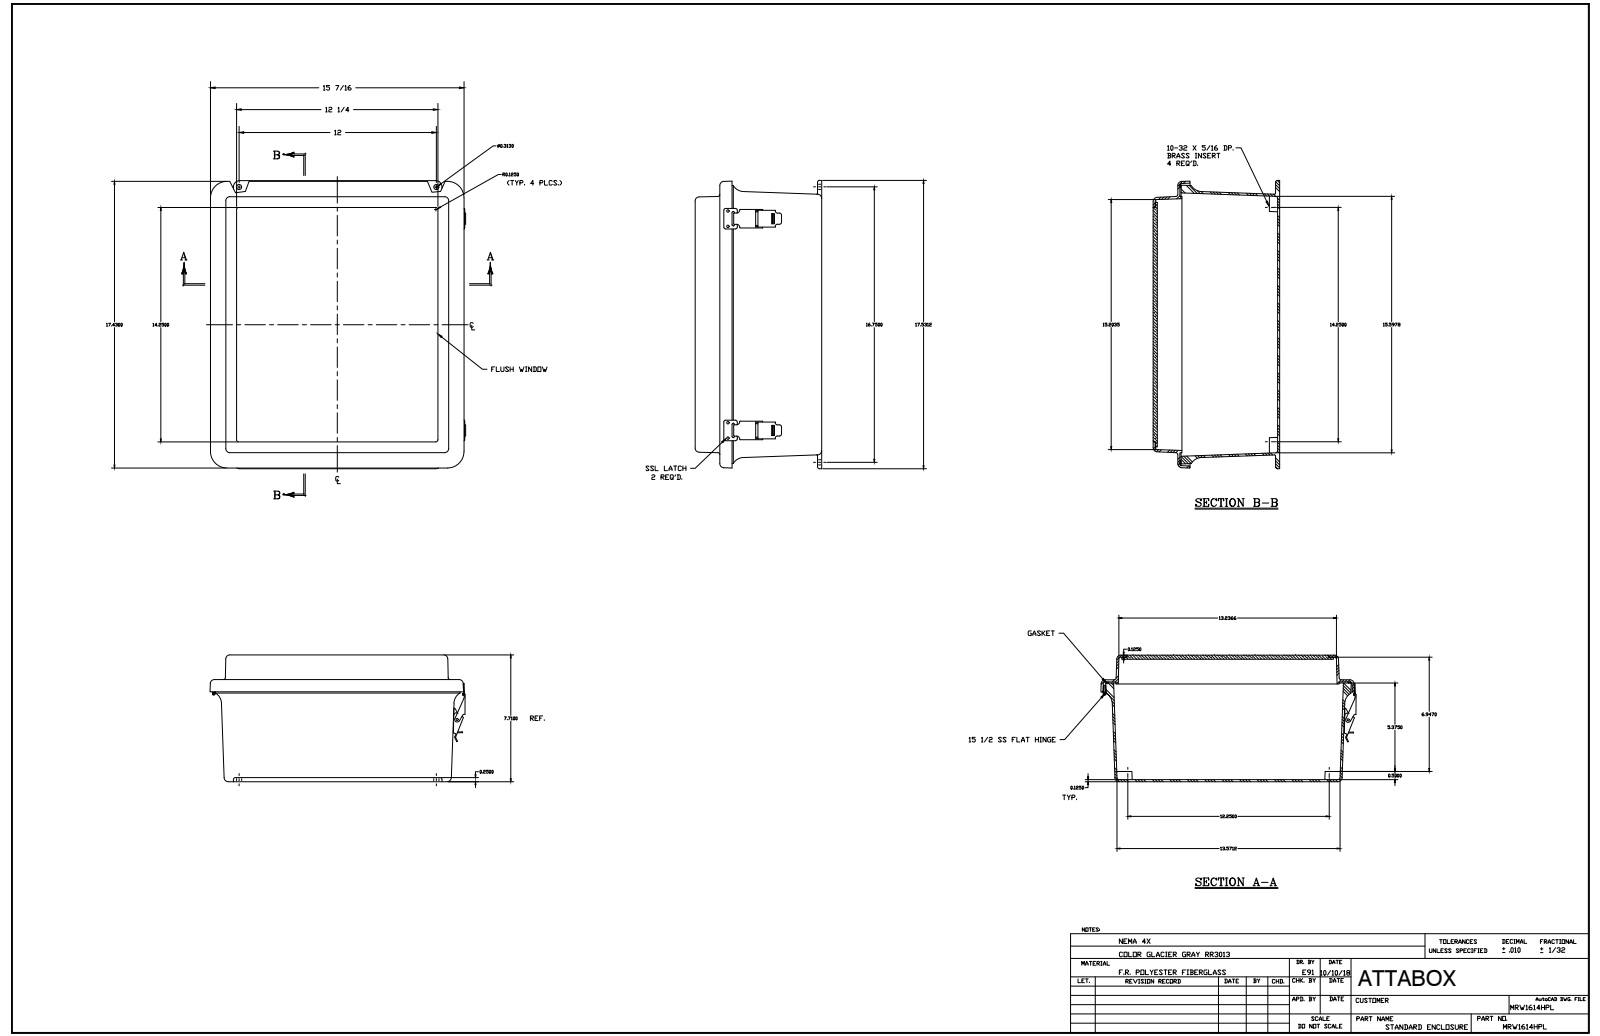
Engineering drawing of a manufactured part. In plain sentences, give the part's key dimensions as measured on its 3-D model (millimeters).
The part is named "MRW1614HPL". Its 3-D file was written by "SolidWorks 2018 (AUTOMOTIVE_DESIGN)". It is 41 solids with 1180 faces: 519 planar, 488 cylindrical and 173 other. Overall it measures 445.3 by 395.4 by 195.5 millimeters. Its volume is 2 809 000 cubic millimeters and its surface area 1 411 000 square millimeters. Round holes: 22 of diameter 3.6, 10 of diameter 3.3, 8 of diameter 2.6, 8 of diameter 3.9, 4 of diameter 3.3, 4 of diameter 4, 4 of diameter 5.5, 2 of diameter 3.4, 2 of diameter 9.5, 1 of diameter 2.2. Round bosses or shafts: 12 of diameter 3.2, 10 of diameter 6.4, 6 of diameter 3.2, 4 of diameter 6.9, 1 of diameter 7.6, 1 of diameter 4.3, 1 of diameter 3.9, 1 of diameter 3.9. Partial cylindrical surfaces (rounded edges, fillets, slot ends): 32 of radius 3.2, 20 of radius 0.4, 20 of radius 0.8, 20 of radius 6.4, 16 of radius 1.1, 12 of radius 0.8, 8 of radius 0.6, 6 of radius 1.5. The main face-to-face distances are 3.2, 189.2, 3.2, 6.4, 195.5, 192.3, 186, 151, 38.2, 154.2. The hole center spacings are 95.3, 190.5, 326.9, 23.8, 326.8, 6.4, 19.1, 285.8.
